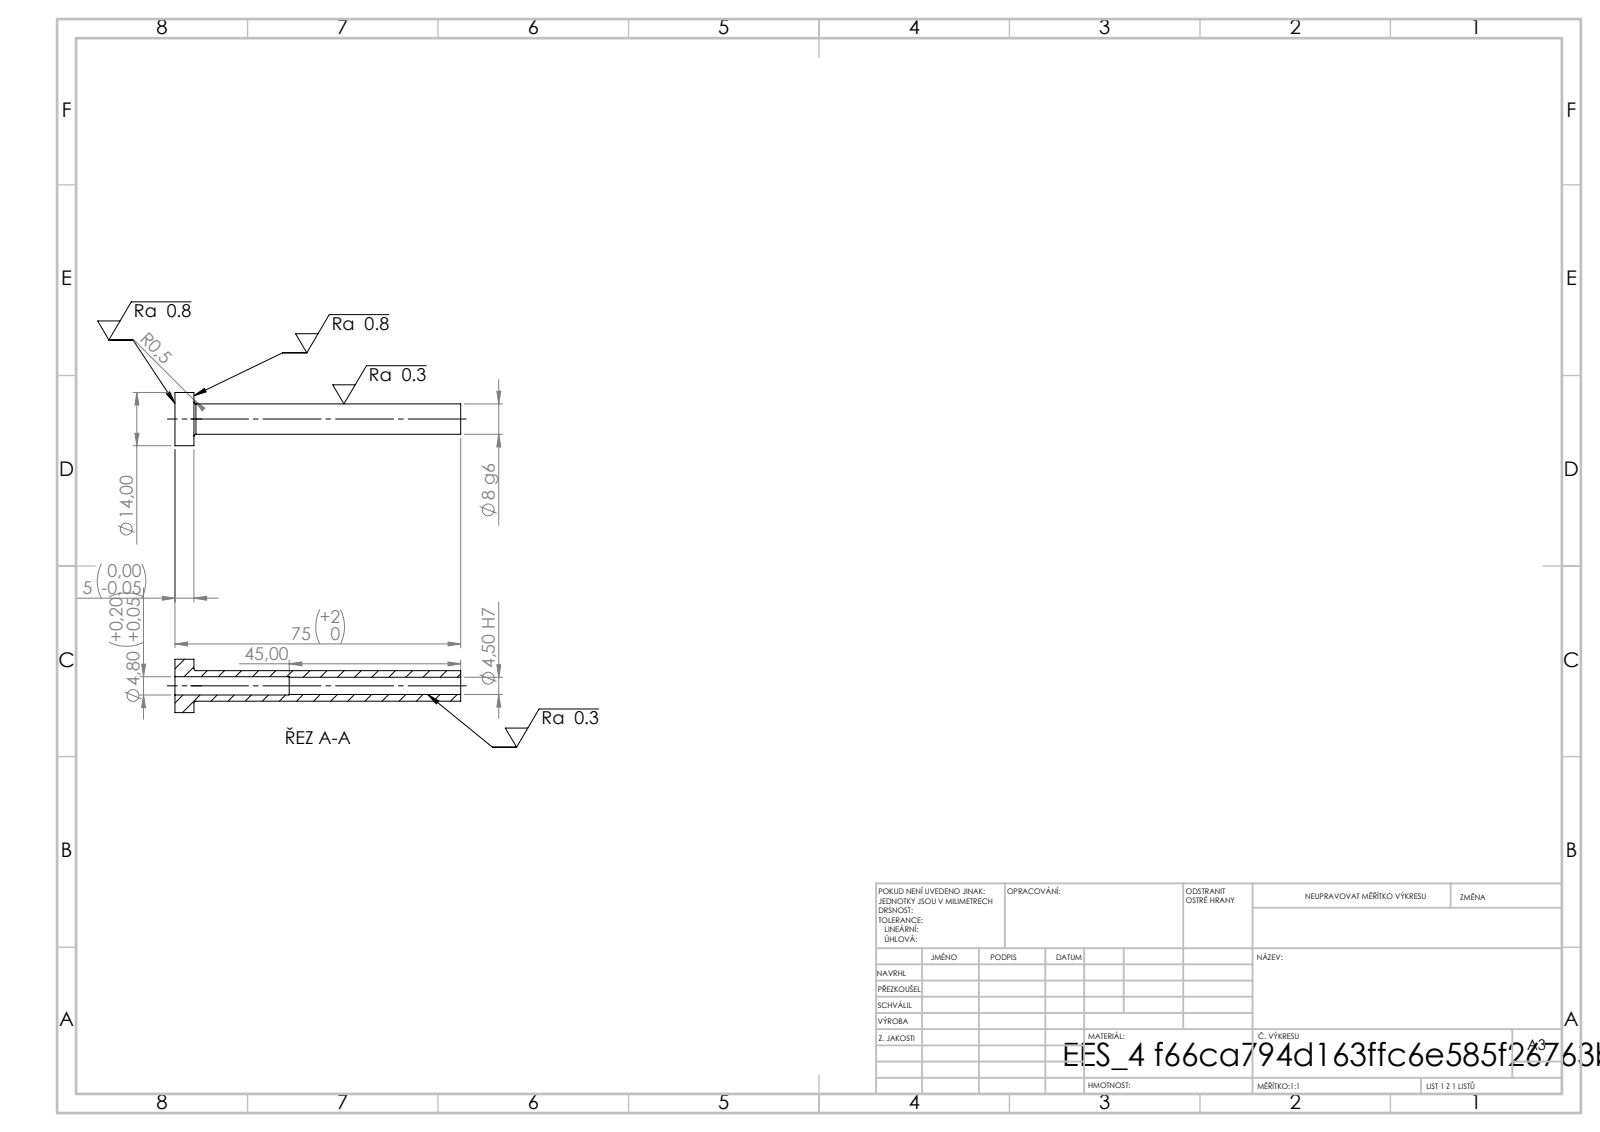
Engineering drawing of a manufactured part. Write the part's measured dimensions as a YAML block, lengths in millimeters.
step_written_by: "SolidWorks 2019 (CONFIG_CONTROL_DESIGN)"
units: millimeters
bodies: {solids: 1, faces: 14, planar: 4, cylindrical: 8, other: 2}
overall_size: [75, 14, 14]
volume: 3031
surface_area: 3339
round_holes:
  - {diameter: 4.5, count: 1}
  - {diameter: 4.8, count: 1}
round_bosses_or_shafts:
  - {diameter: 14, count: 1}
  - {diameter: 8, count: 1}
face_to_face_distances: [5, 75, 70, 30, 25, 45]
